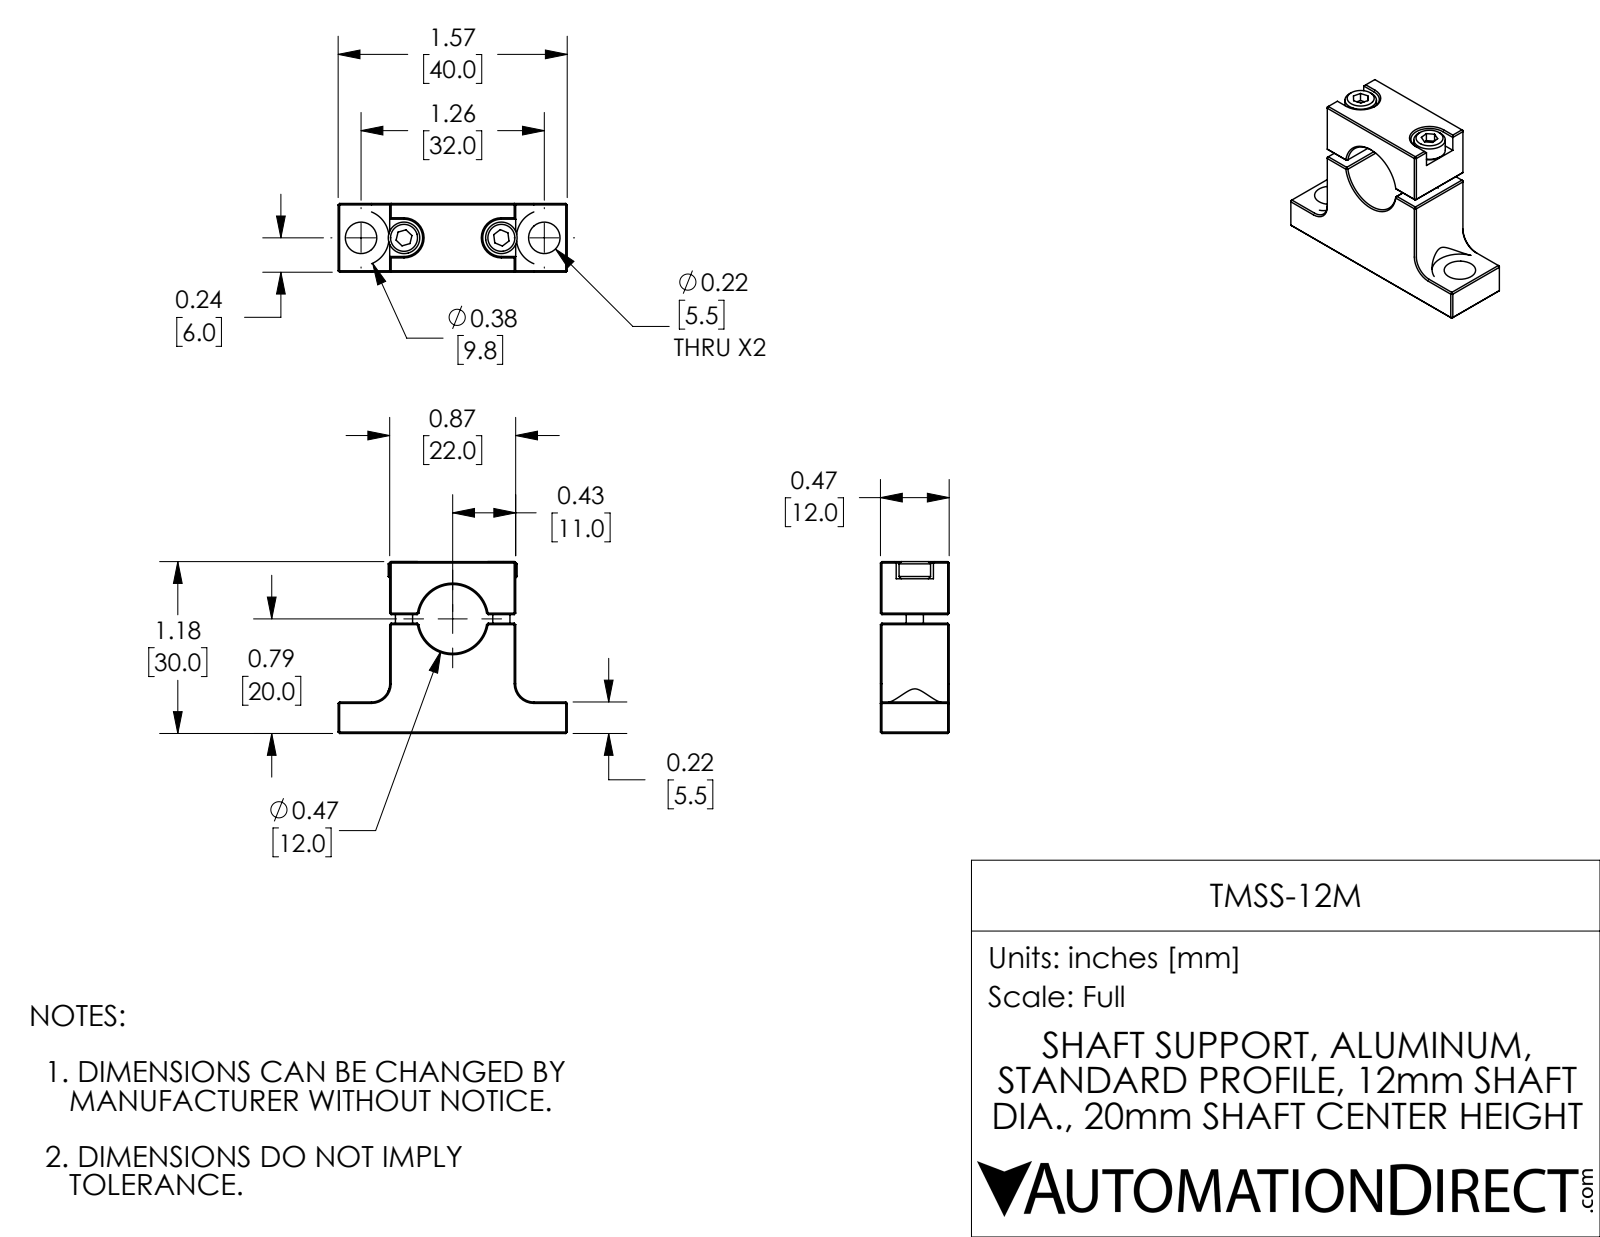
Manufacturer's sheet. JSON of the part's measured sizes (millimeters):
{"part_name": "TMSS-12M", "step_written_by": "SolidWorks 2017 (AUTOMOTIVE_DESIGN)", "units": "millimeters", "bodies": {"solids": 4, "faces": 177, "planar": 120, "cylindrical": 31, "other": 26}, "overall_size": [40, 30, 12], "volume_mm3": 7110, "surface_area_mm2": 4436, "round_holes": [[2.5, 2], [3.4, 2], [5.5, 2], [2.4, 1], [12, 1]], "round_bosses_or_shafts": [[5.5, 2], [3, 2]], "partial_cylinders_radius": [[3.2, 2], [3.3, 2], [4.9, 2]], "face_to_face_distances": [12, 22, 30, 9.2, 5.5, 24.5, 9, 31, 1.5, 19.3], "hole_center_spacings": [7.5, 8.5, 16, 24.5, 17, 32]}
